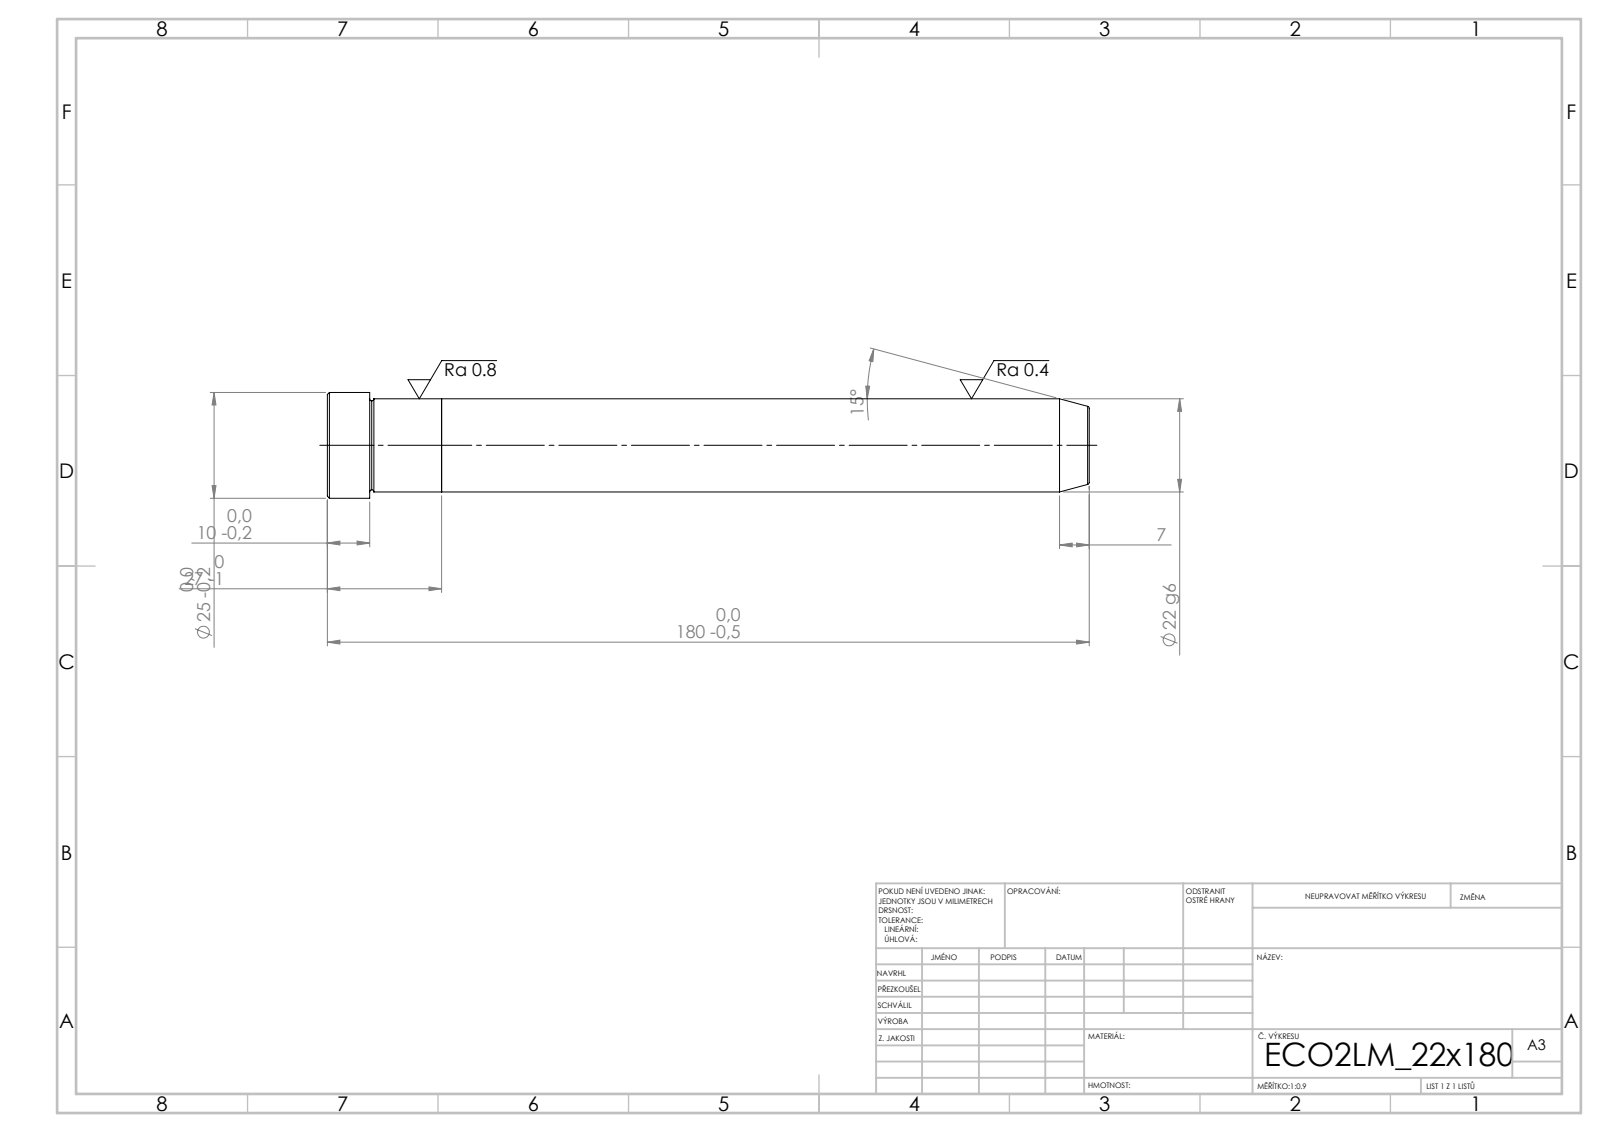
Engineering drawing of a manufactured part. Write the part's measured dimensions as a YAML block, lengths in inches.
step_written_by: "SolidWorks 2019 (CONFIG_CONTROL_DESIGN)"
units: inches
bodies: {solids: 2, faces: 21, planar: 5, cylindrical: 6, other: 10}
overall_size: [7.087, 0.984, 0.984]
volume: 4.215
surface_area: 21.92
round_bosses_or_shafts:
  - {diameter: 0.984, count: 1}
  - {diameter: 0.866, count: 1}
face_to_face_distances: [1.063, 6.024, 7.087, 6.693, 0.669, 0.394]
